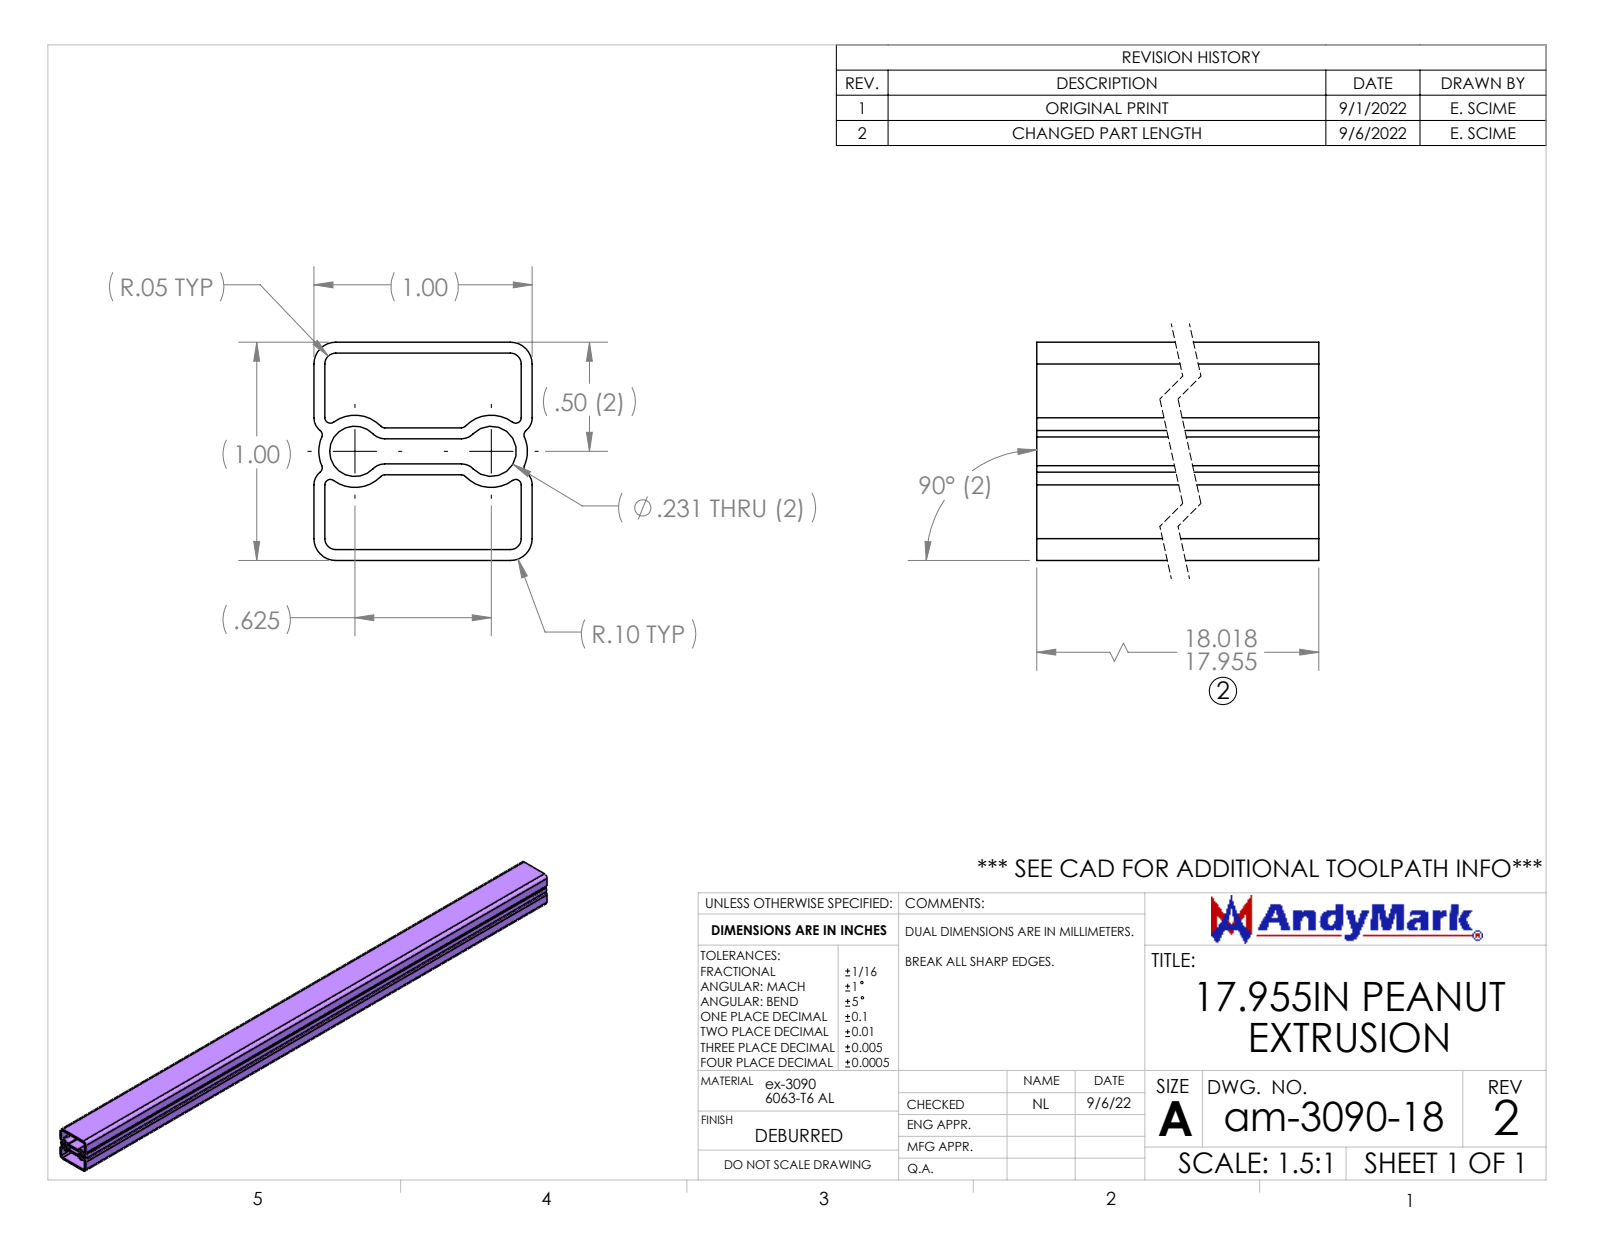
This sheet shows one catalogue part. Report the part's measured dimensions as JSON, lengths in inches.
{"part_name": "am-3090-18 17.955IN Peanut Extrusion", "step_written_by": "SolidWorks 2022 (CONFIG_CONTROL_DESIGN)", "units": "inches", "bodies": {"solids": 1, "faces": 428, "planar": 22, "cylindrical": 160, "other": 246}, "overall_size": [17.955, 1, 1], "volume_in3": 4.925, "surface_area_in2": 195.9, "partial_cylinders_radius": [[0.025, 12], [0.075, 8], [0.05, 4], [0.1, 4], [0.116, 2], [0.166, 2]], "face_to_face_distances": [0.05, 0.95, 0.392, 0.558, 0.9, 1, 0.442, 0.608, 0.342, 0.508]}
